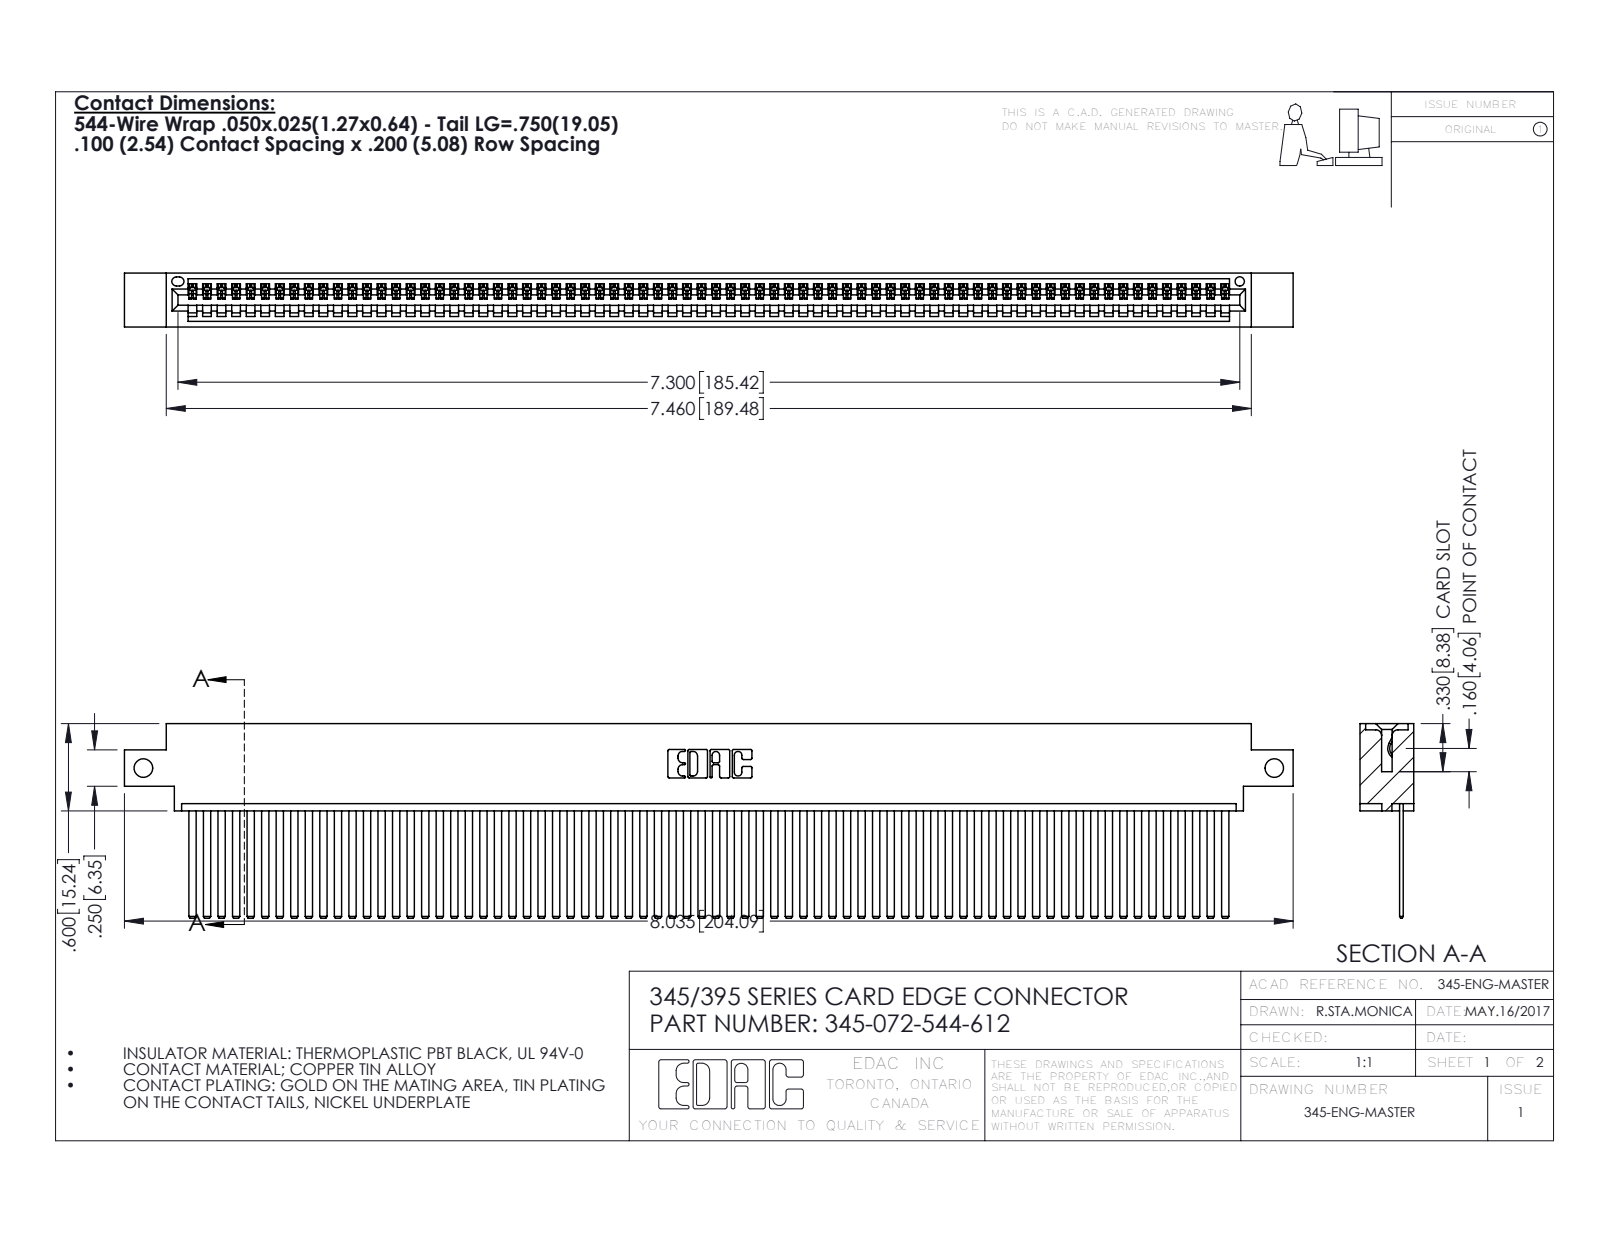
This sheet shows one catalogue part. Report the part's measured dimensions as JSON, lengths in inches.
{"part_name": "345-072-544-612; 345-292-001_345-293-144; 345 Part_0.170 Offset - Side Mount", "step_written_by": "SolidWorks 2016 (CONFIG_CONTROL_DESIGN)", "units": "inches", "bodies": {"solids": 73, "faces": 3874, "planar": 2676, "cylindrical": 1198, "other": 0}, "overall_size": [8.035, 1.337, 0.37], "volume_in3": 1.237, "surface_area_in2": 46.23, "round_holes": [[0.128, 2], [0.064, 1]], "partial_cylinders_radius": [[0.006, 144], [0.01, 22], [0.007, 6], [0.031, 6], [0.026, 3], [0.031, 2], [0.04, 2], [0.014, 1]], "face_to_face_distances": [0.072, 0.298, 0.025, 0.098, 0.272, 0.37, 0.2, 0.225, 0.175, 0.149], "hole_center_spacings": [7.775]}
